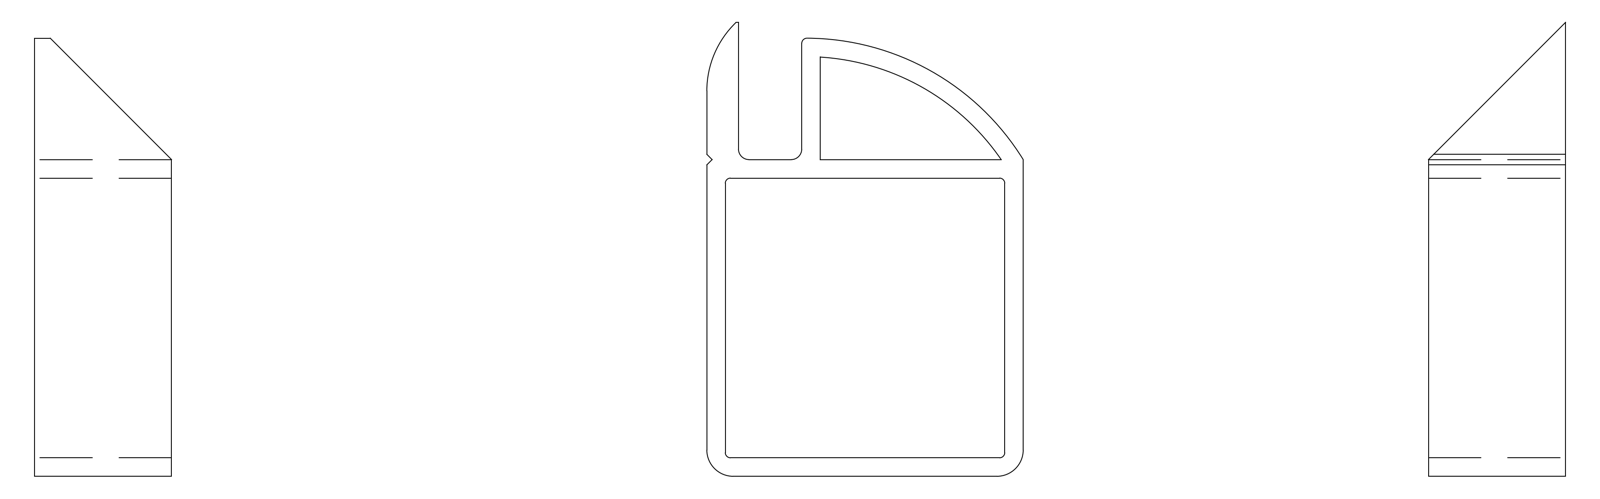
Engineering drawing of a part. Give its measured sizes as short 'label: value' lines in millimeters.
written by: THINKDESIGN (CONFIG_CONTROL_DESIGN)
unit: mm
bodies: 1 solid, 32 faces (20 planar, 12 cylindrical, 0 other)
size: 43 × 30 × 13
volume: 3 866 mm³; area: 3 998 mm²
rounds: 5× R0.5, 2× R1, 2× R2.5, 1× R9, 1× R22.51, 1× R24.26
face distances: 1.75, 28.25, 26.5, 30, 13, 3, 10, 9, 19.25, 1.25
